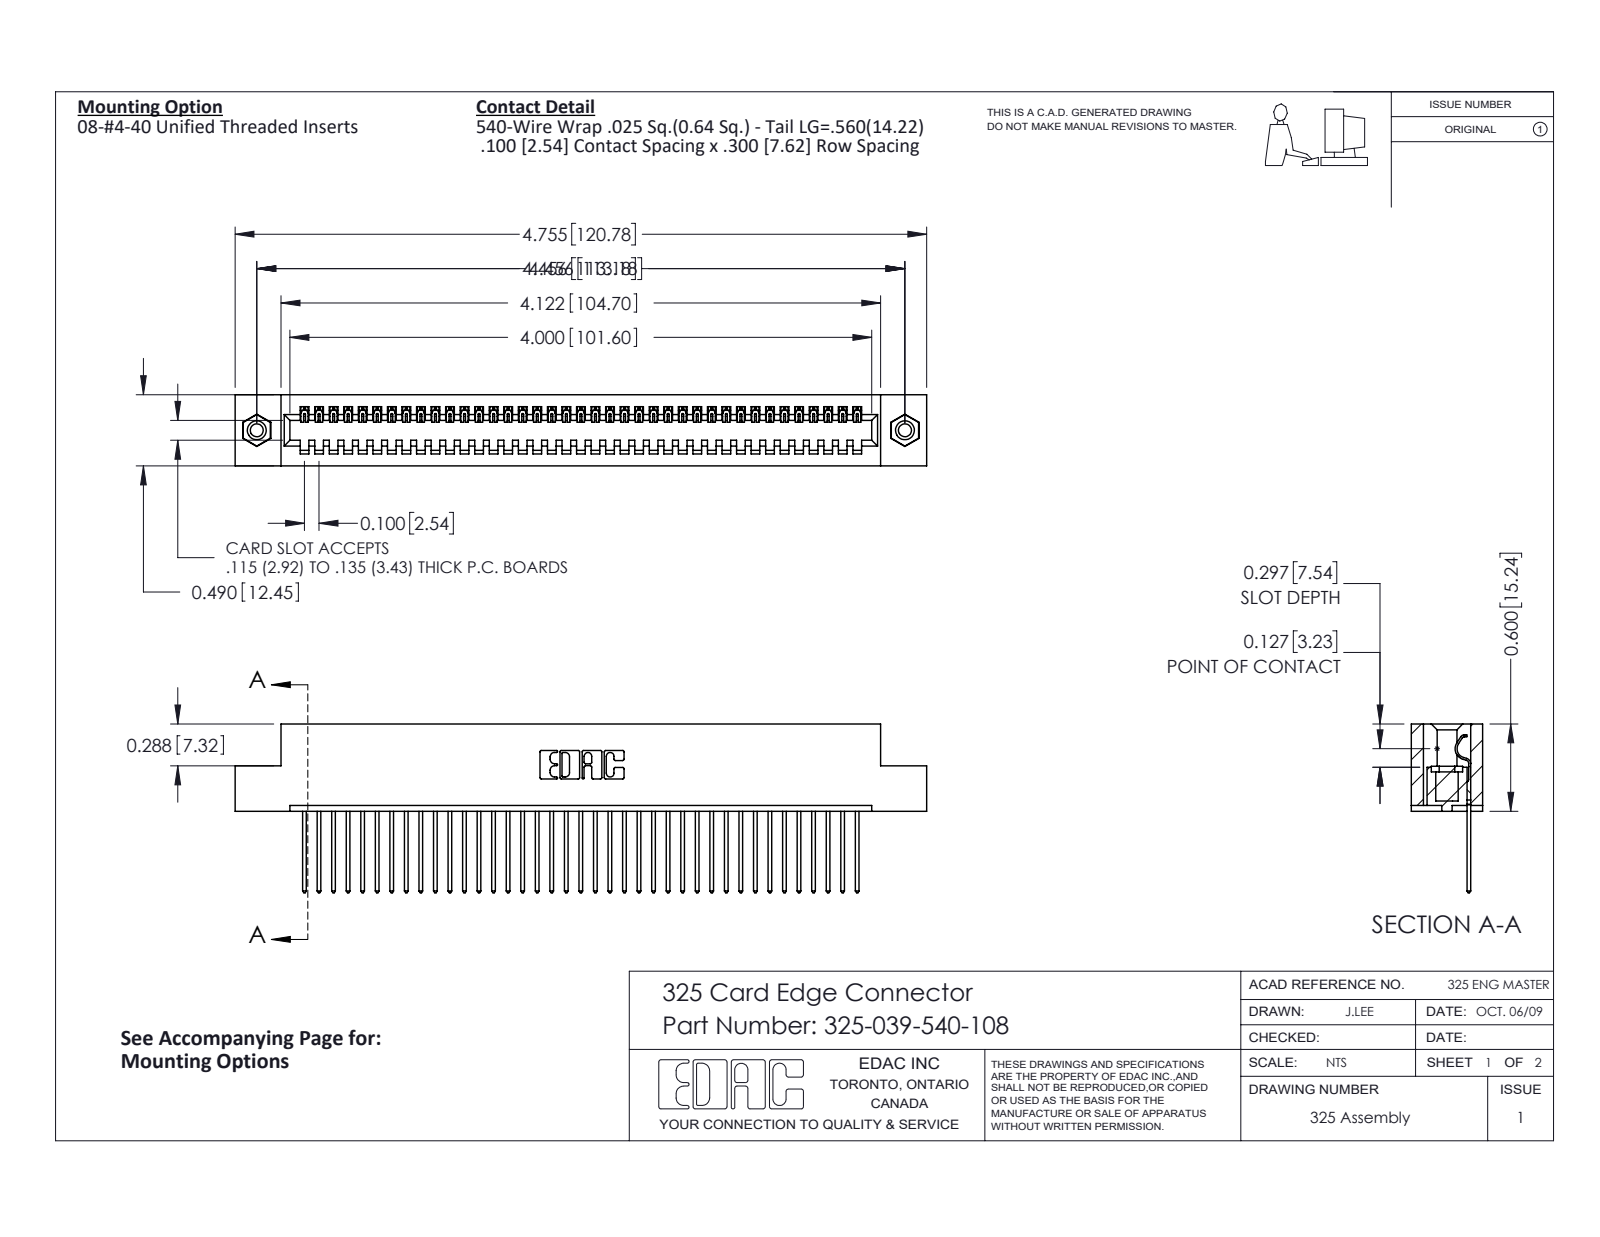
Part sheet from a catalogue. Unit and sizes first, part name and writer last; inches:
Units: inches
Overall size (bounding box): 4.755 × 1.16 × 0.49
Round holes (diameter × count): ⌀0.089 ×2, ⌀0.125 ×2, ⌀0.16 ×2
Round bosses / shafts (diameter × count): ⌀0.155 ×2
Partial cylindrical surfaces — rounded edges, fillets, slot ends (radius × count): R0.006 ×78, R0.01 ×78, R0.01 ×22, R0.007 ×6, R0.031 ×6, R0.026 ×3, R0.014 ×1, R0.022 ×1
Main face-to-face distances: 0.083, 0.407, 0.49, 0.3, 0.107, 0.383, 0.025, 0.325, 0.56, 0.04
Hole centre spacings: 4.456
Volume: 0.937 in³ · Surface area: 26.55 in²
Bodies: 42 solids, 2436 faces (1740 planar, 680 cylindrical, 16 other)
Part name (STEP PRODUCT): 345-250-001_345-250-003-102; 325 Part_TI; 325-039-540-108; 325-292-001_325-293-140
STEP written by: SolidWorks 2016 (CONFIG_CONTROL_DESIGN)
